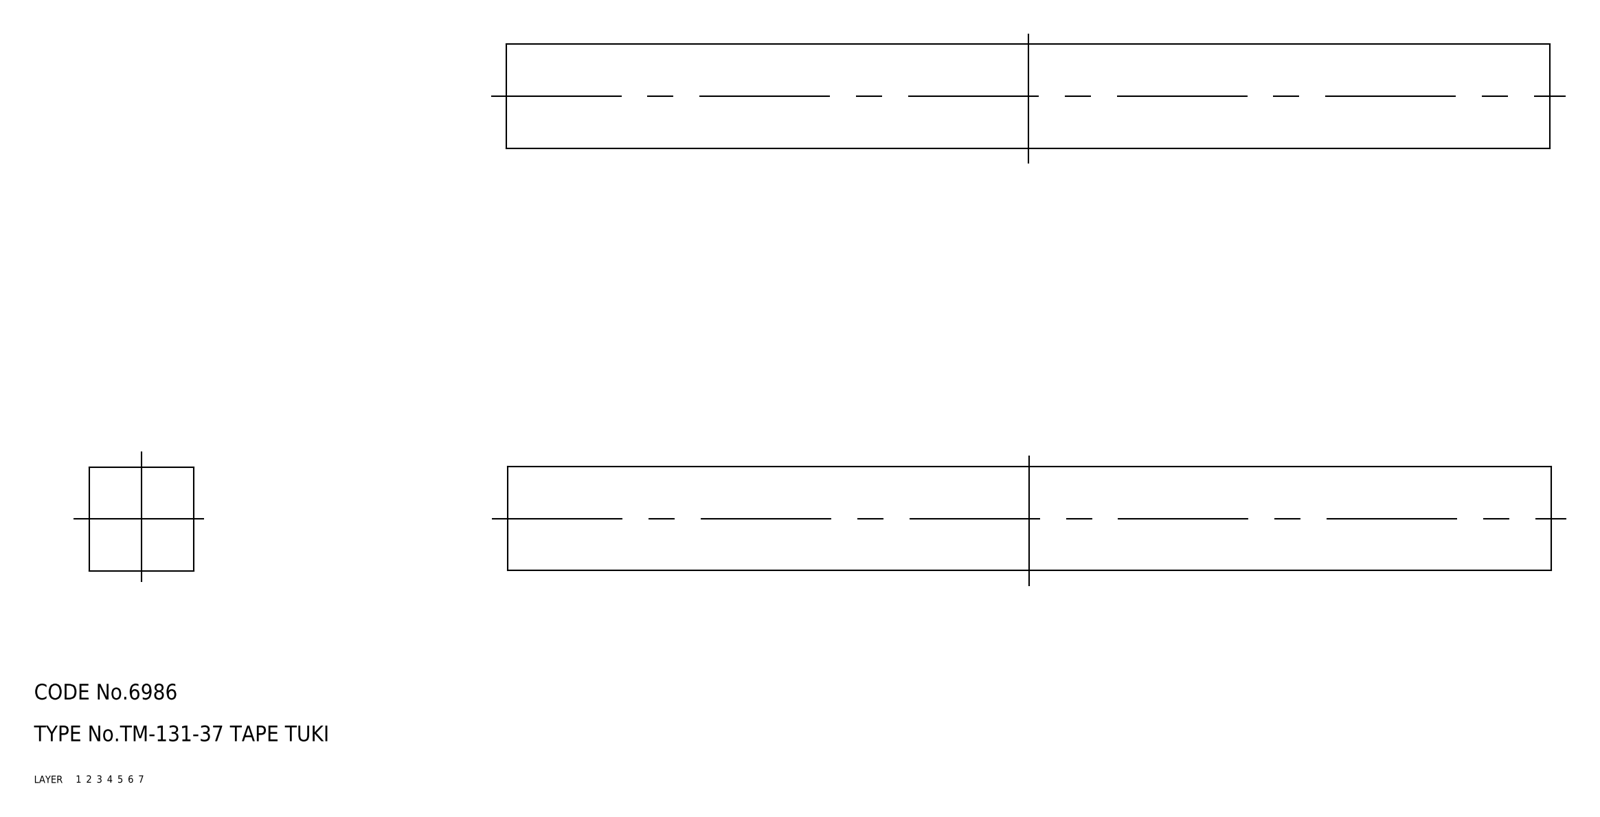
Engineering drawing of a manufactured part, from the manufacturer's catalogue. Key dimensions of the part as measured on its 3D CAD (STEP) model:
Part name (STEP PRODUCT): rubber foam
STEP written by: CADfix (AUTOMOTIVE_DESIGN)
Units: millimetres
Bodies: 1 solid, 6 faces (0 planar, 0 cylindrical, 6 other)
Overall size (bounding box): 200 × 20 × 20
Volume: 80 000 mm³ · Surface area: 16 800 mm²
